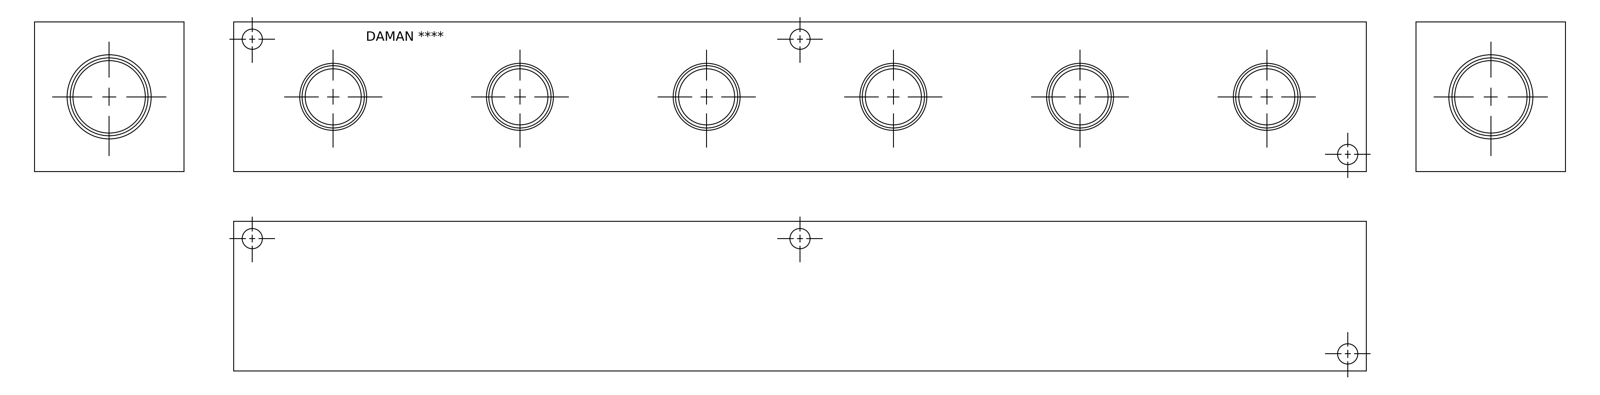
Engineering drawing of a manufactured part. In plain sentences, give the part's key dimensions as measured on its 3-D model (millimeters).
The part is named "Part_+H0000616P_3D". Its 3-D file was written by "Autodesk Inventor 2019 (AUTOMOTIVE_DESIGN)". It is 1 solid with 357 faces: 218 planar, 28 cylindrical and 111 other. Overall it measures 577.85 by 76.2 by 76.2 millimeters. Its volume is 3 139 000 cubic millimeters and its surface area 219 595 square millimeters. Round holes: 6 of diameter 10.31, 6 of diameter 28.57, 6 of diameter 33.71, 1 of diameter 36.91, 1 of diameter 42.47. The main face-to-face distances are 76.2, 577.85, 57.2, 19, 19.51, 558.34, 538.83, 75.2, 18, 1. The hole center spacings are 95.25, 190.5, 285.75, 279.4, 285.5, 381, 561.88, 50.65.
